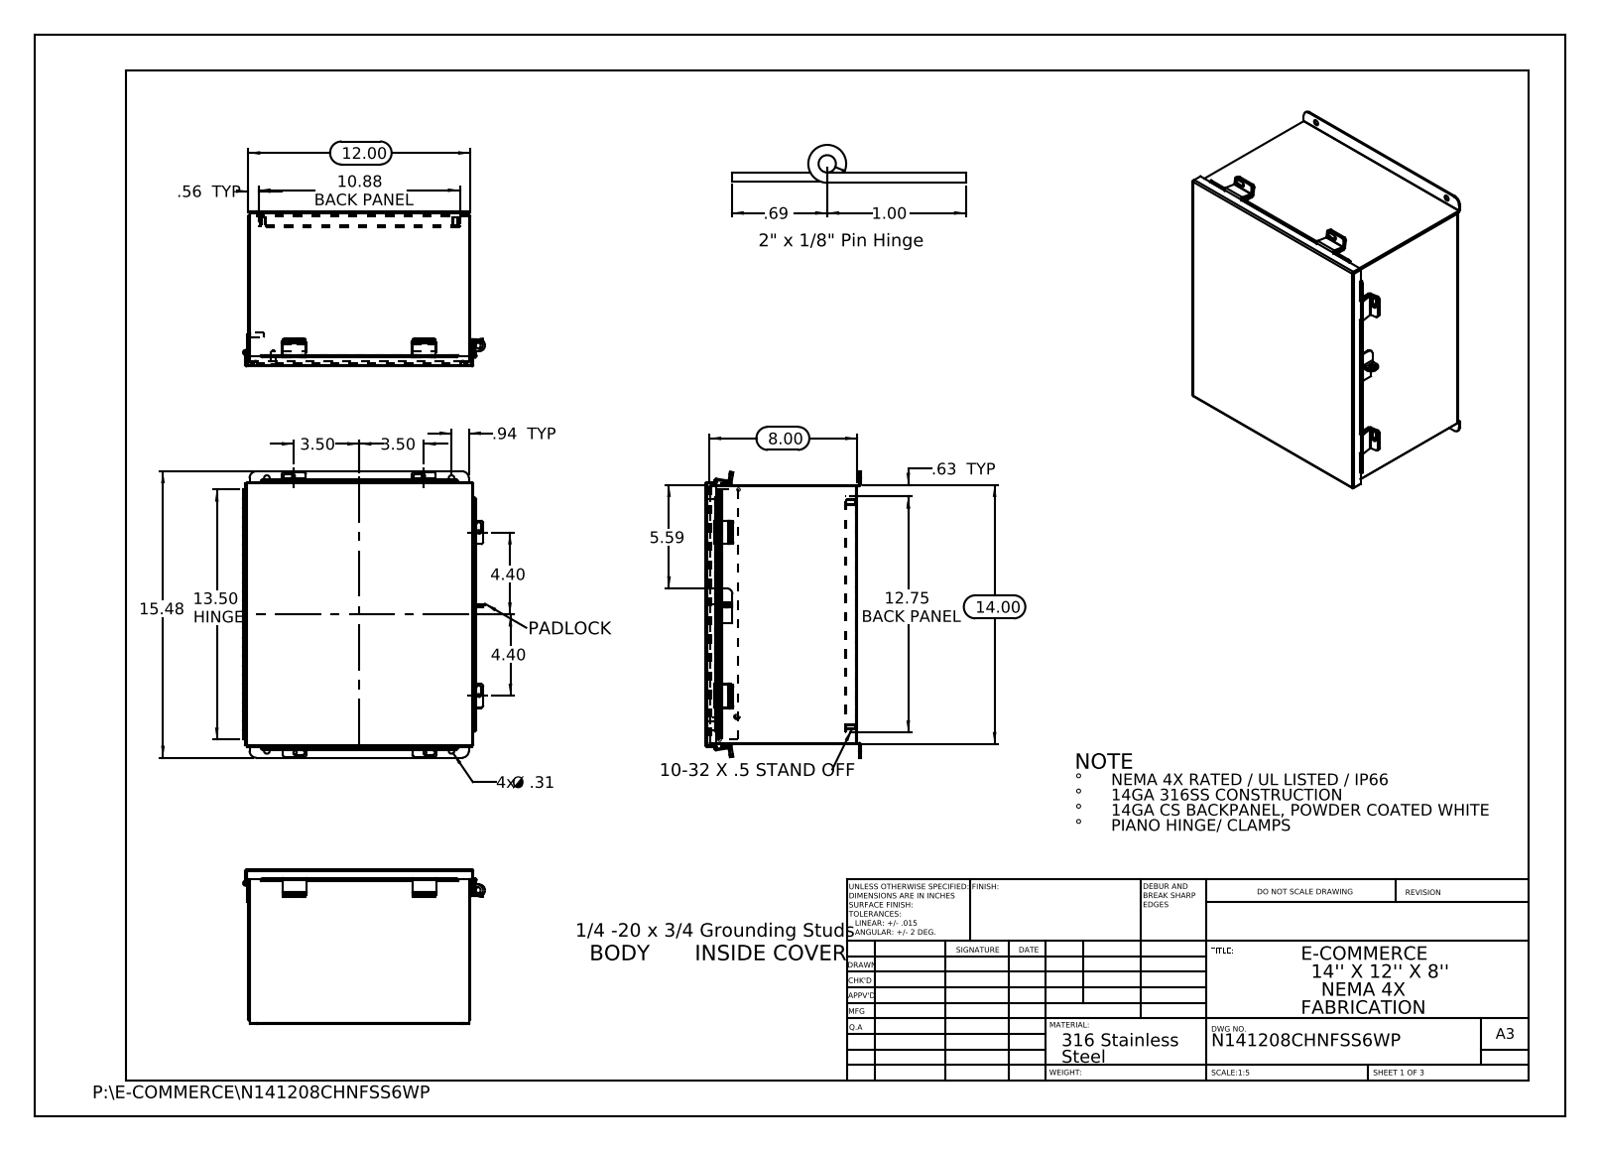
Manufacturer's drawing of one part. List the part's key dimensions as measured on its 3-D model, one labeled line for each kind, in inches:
Part name (STEP PRODUCT): N141208CHNFSS6WP JIC Clamp Bracket; HW-CLH-JH-20104; HW-CLH-JH-20154; N141208CHNFSS6WP JIC_Standoff (+8 more)
STEP written by: SolidWorks 2013 (CONFIG_CONTROL_DESIGN)
Units: inches
Bodies: 27 solids, 830 faces (519 planar, 291 cylindrical, 20 other)
Overall size (bounding box): 15.476 × 13.072 × 8.39
Volume: 75.12 in³ · Surface area: 2 044 in²
Round holes (diameter × count): ⌀0.25 ×10, ⌀0.187 ×4, ⌀0.312 ×4, ⌀0.125 ×1, ⌀0.125 ×1, ⌀0.373 ×1, ⌀0.375 ×1
Round bosses / shafts (diameter × count): ⌀0.313 ×4, ⌀0.315 ×2, ⌀0.236 ×2, ⌀0.273 ×1, ⌀0.25 ×1
Partial cylindrical surfaces — rounded edges, fillets, slot ends (radius × count): R0.125 ×21, R0.013 ×13, R0.009 ×12, R0.088 ×12, R0.133 ×12, R0.083 ×6, R0.1 ×6, R0.375 ×4
Main face-to-face distances: 0.075, 8.128, 11.925, 13.925, 8.053, 8.203, 0.575, 0.5, 7.553, 7.628
Hole centre spacings: 1.315, 10.258, 13.428, 16.846, 7, 9.976, 10.375, 12.126
